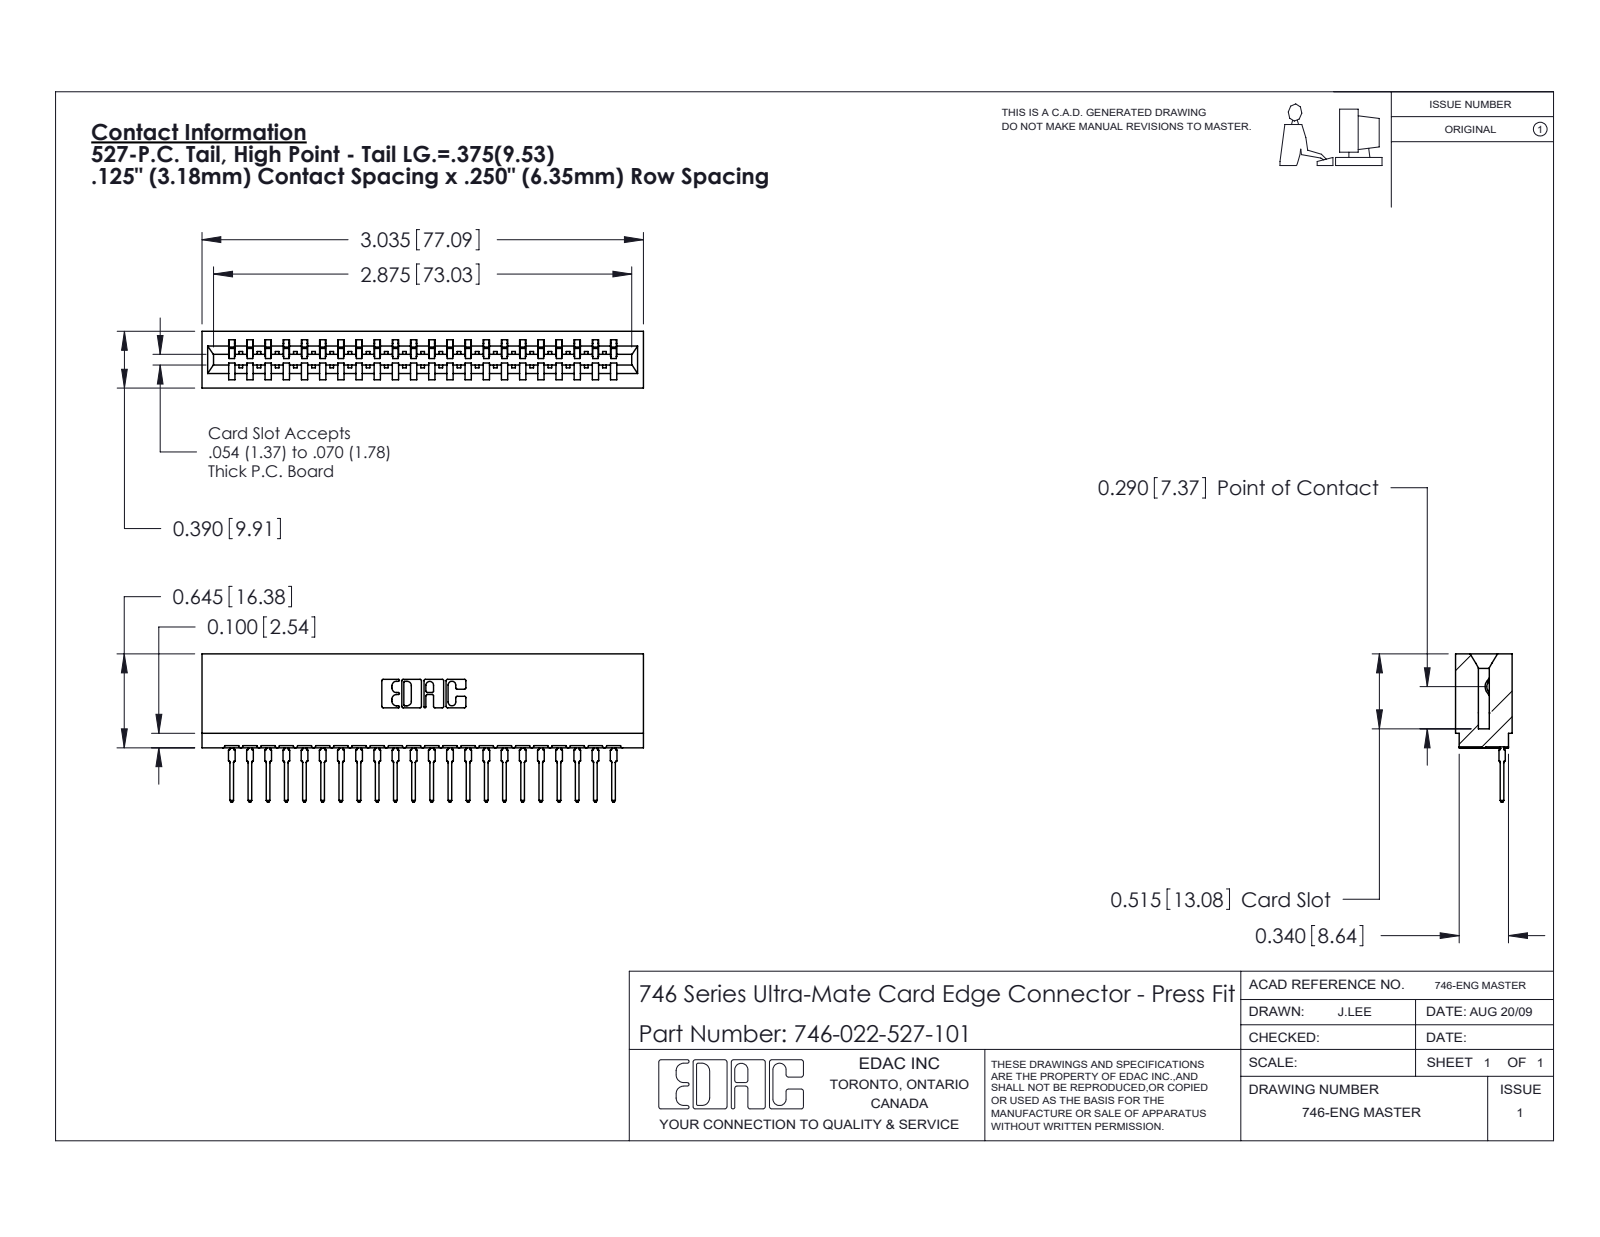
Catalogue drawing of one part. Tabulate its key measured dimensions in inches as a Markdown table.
| quantity | value |
| --- | --- |
| part name | 746-292-001_527; 746 Part_.515 Slot Depth - 01; 746-022-527-101 |
| STEP written by | SolidWorks 2020 (CONFIG_CONTROL_DESIGN) |
| units | inches |
| bodies | 23 solids, 2473 faces (1441 planar, 460 cylindrical, 572 other) |
| overall size | 3.035 × 1.019 × 0.39 |
| volume | 0.501 in³ |
| surface area | 18.54 in² |
| partial cylindrical surfaces (radius × count) | 0.021 × 44, 0.015 × 23, 0.01 × 22, 0.007 × 6, 0.031 × 6, 0.005 × 4, 0.011 × 4, 0.026 × 3 |
| main face-to-face distances | 0.057, 0.333, 0.25, 0.39, 0.5, 0.025, 0.307, 0.125, 0.125, 0.375 |
